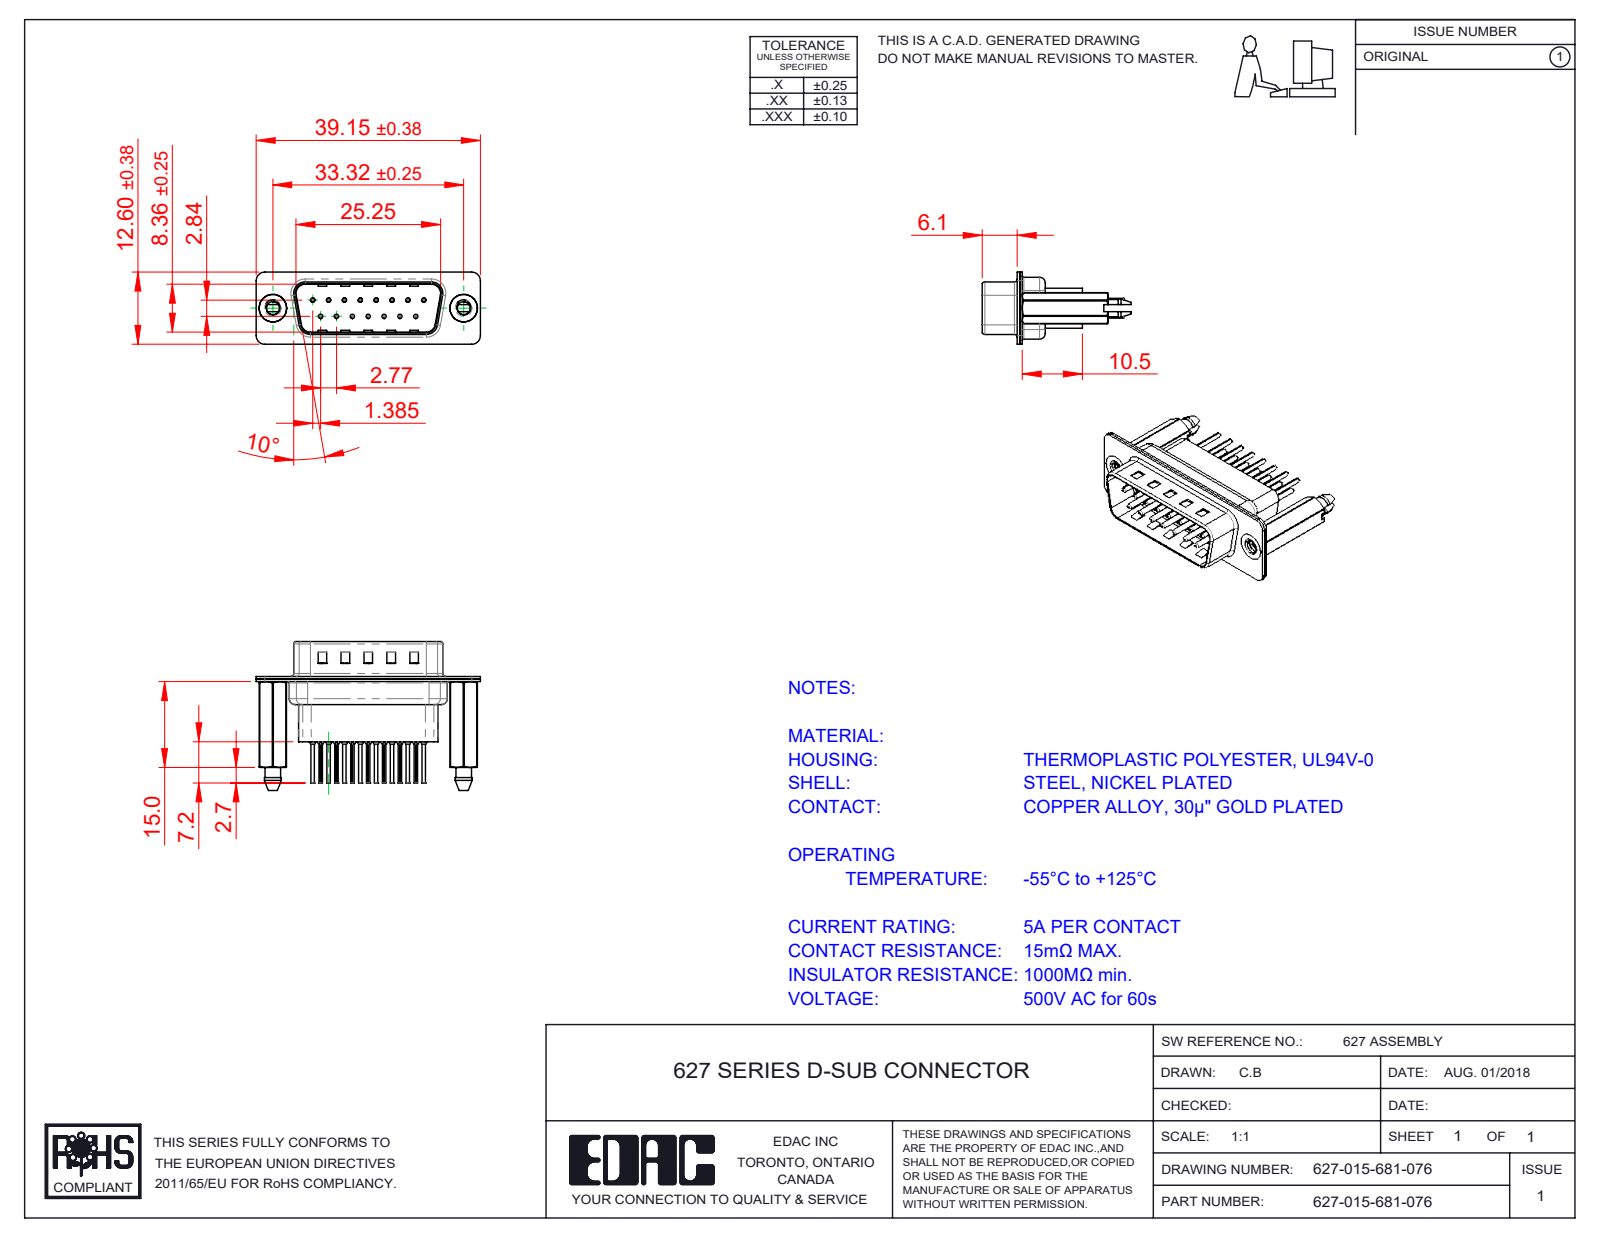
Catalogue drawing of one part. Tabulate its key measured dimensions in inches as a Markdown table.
| quantity | value |
| --- | --- |
| part name | 627 Contact Row 1_61; 627 4-40 Threaded Boardlock_HP81; 627 Shell Rear_15 Contacts; 627 Contact Row 2_61 (+3 more) |
| STEP written by | SolidWorks 2020 (CONFIG_CONTROL_DESIGN) |
| units | inches |
| bodies | 20 solids, 1918 faces (531 planar, 754 cylindrical, 633 other) |
| overall size | 1.541 × 1.02 × 0.496 |
| volume | 0.179 in³ |
| surface area | 11.71 in² |
| round holes (diameter × count) | 0.008 × 15, 0.014 × 15, 0.043 × 15, 0.063 × 15, 0.089 × 2, 0.157 × 2, 0.189 × 2 |
| round bosses / shafts (diameter × count) | 0.079 × 15, 0.059 × 15, 0.03 × 15, 0.024 × 15, 0.193 × 2 |
| partial cylindrical surfaces (radius × count) | 0.004 × 30, 0.059 × 18, 0.079 × 12, 0.063 × 10, 0.02 × 8, 0.01 × 4, 0.024 × 4, 0.026 × 4 |
| main face-to-face distances | 0.016, 0.018, 0.035, 0.032, 0.377, 0.187, 0.059, 0.027, 0.302, 0.055 |
| hole center spacings | 0.124, 0.109, 0.218, 0.327, 0.436, 0.198, 0.198, 0.294 |
